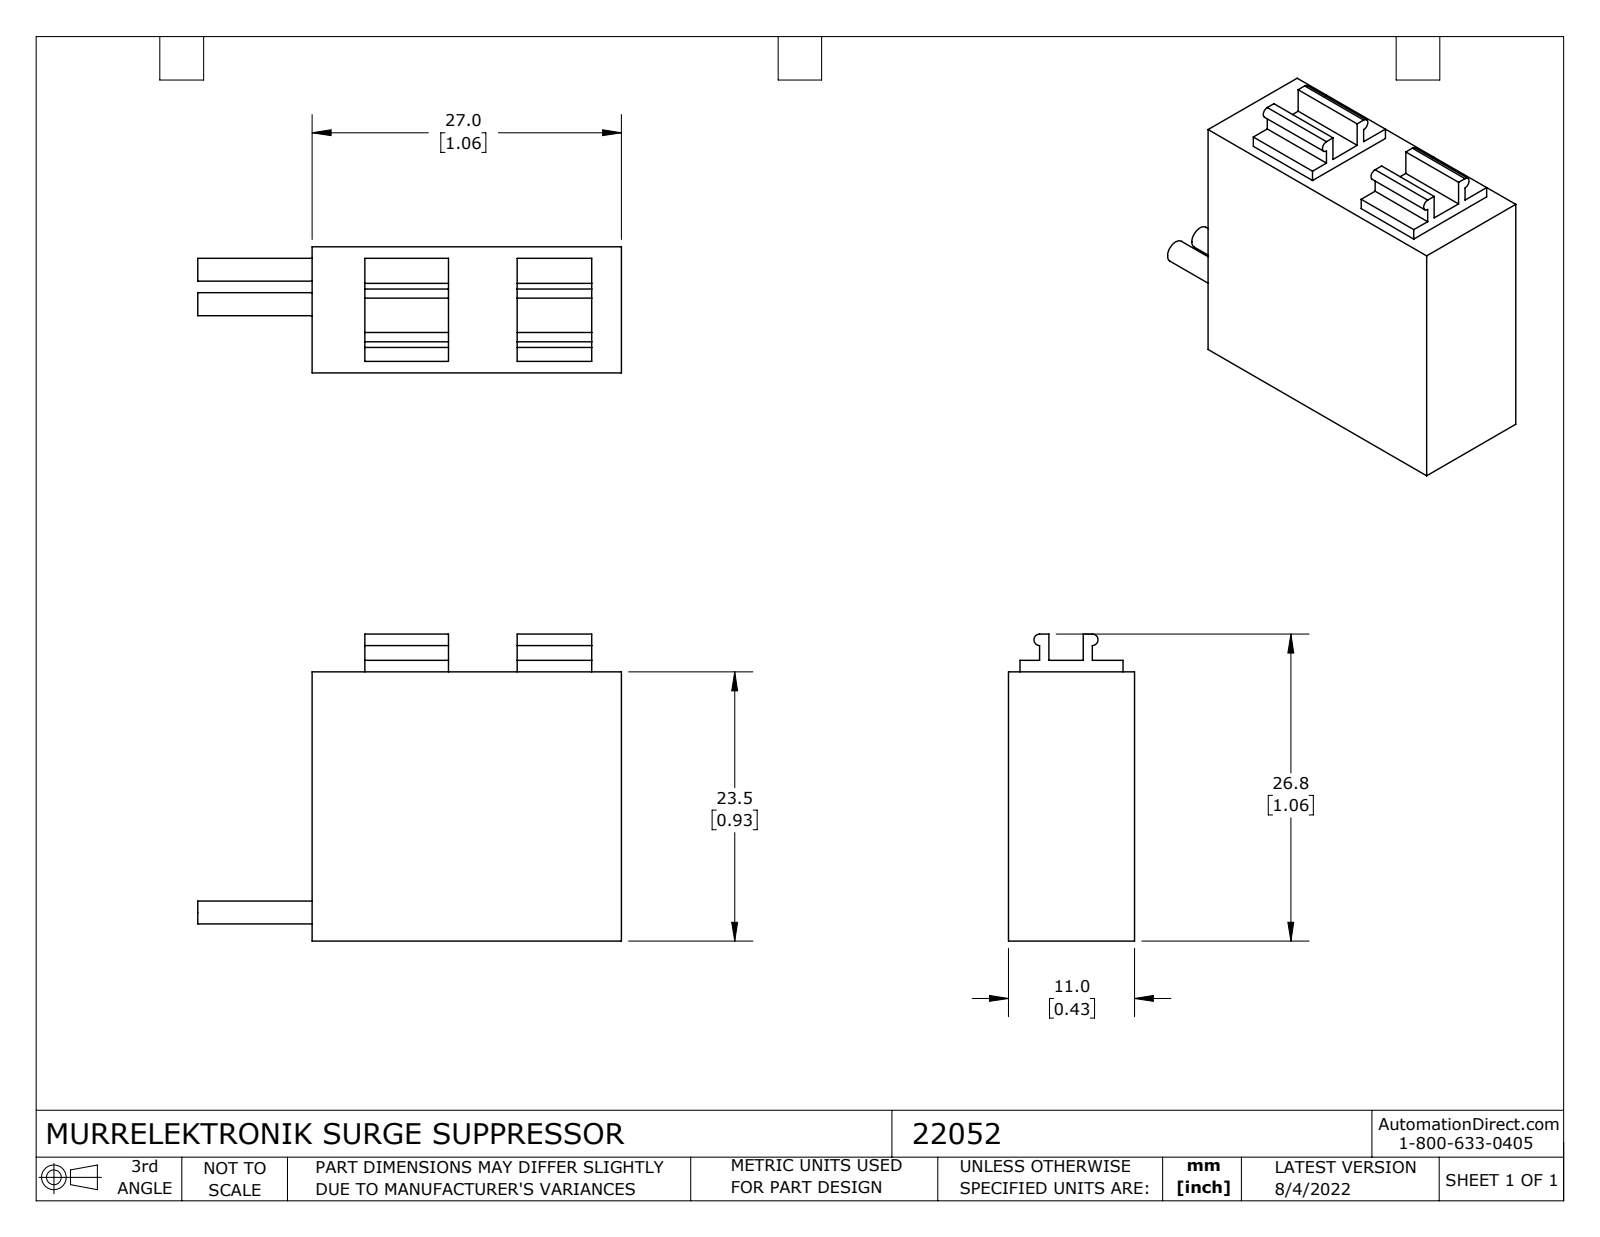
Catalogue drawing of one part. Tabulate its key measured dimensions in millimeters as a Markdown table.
| quantity | value |
| --- | --- |
| part name | 22052 |
| STEP written by | SolidWorks 2021 (CONFIG_CONTROL_DESIGN) |
| units | millimeters |
| bodies | 1 solid, 43 faces (34 planar, 9 cylindrical, 0 other) |
| overall size | 37 × 26.8 × 11 |
| volume | 7 228 mm³ |
| surface area | 2 730 mm² |
| round bosses / shafts (diameter × count) | 2 × 2 |
| partial cylindrical surfaces (radius × count) | 0.5 × 2 |
| main face-to-face distances | 11, 27, 23.5, 1, 24.5, 0.8, 3.8, 10, 4.48, 7.48 |
